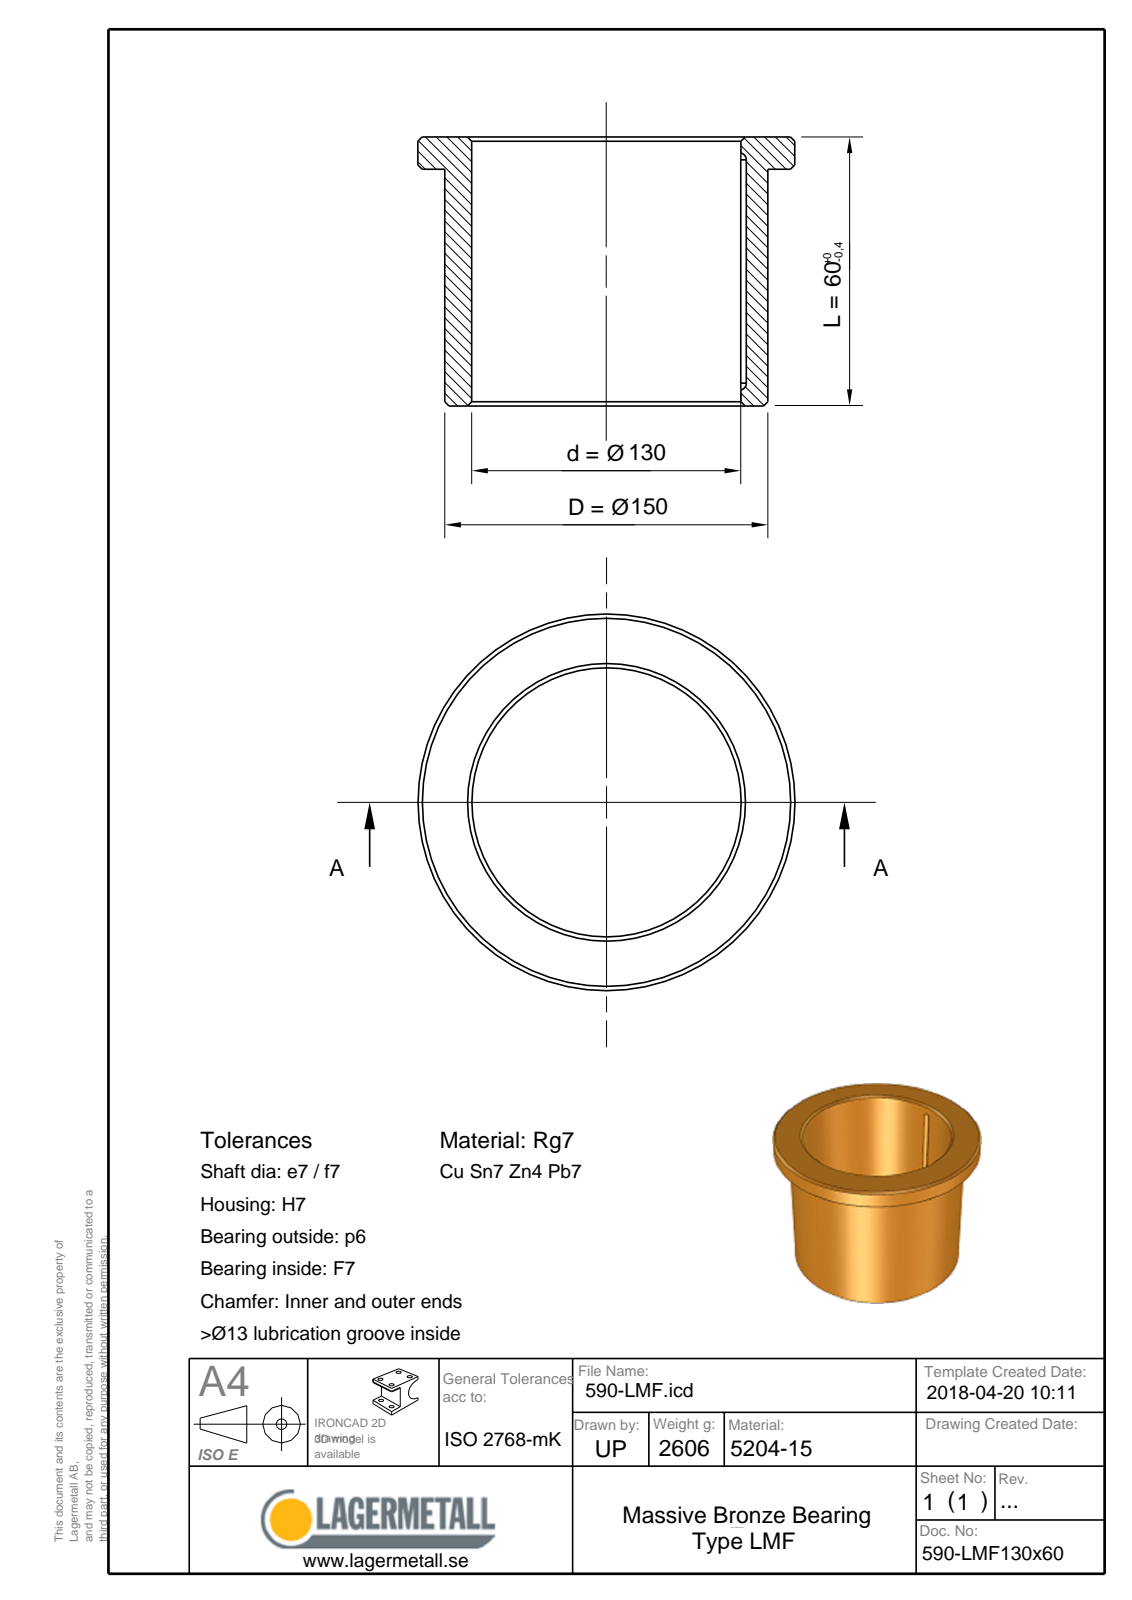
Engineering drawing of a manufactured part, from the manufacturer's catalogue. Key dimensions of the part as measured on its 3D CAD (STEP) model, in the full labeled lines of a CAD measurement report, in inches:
Part name (STEP PRODUCT): 590-LMF130x60
STEP written by: Spatial InterOp 3D (CONFIG_CONTROL_DESIGN)
Units: inches
Bodies: 1 solid, 16 faces (4 planar, 5 cylindrical, 7 other)
Overall size (bounding box): 6.496 × 6.496 × 2.362
Volume: 18.07 in³ · Surface area: 103.6 in²
Round holes (diameter × count): ⌀5.118 ×1
Round bosses / shafts (diameter × count): ⌀6.496 ×1, ⌀5.906 ×1
Partial cylindrical surfaces — rounded edges, fillets, slot ends (radius × count): R0.069 ×2
Main face-to-face distances: 0.394, 1.969, 2.362
